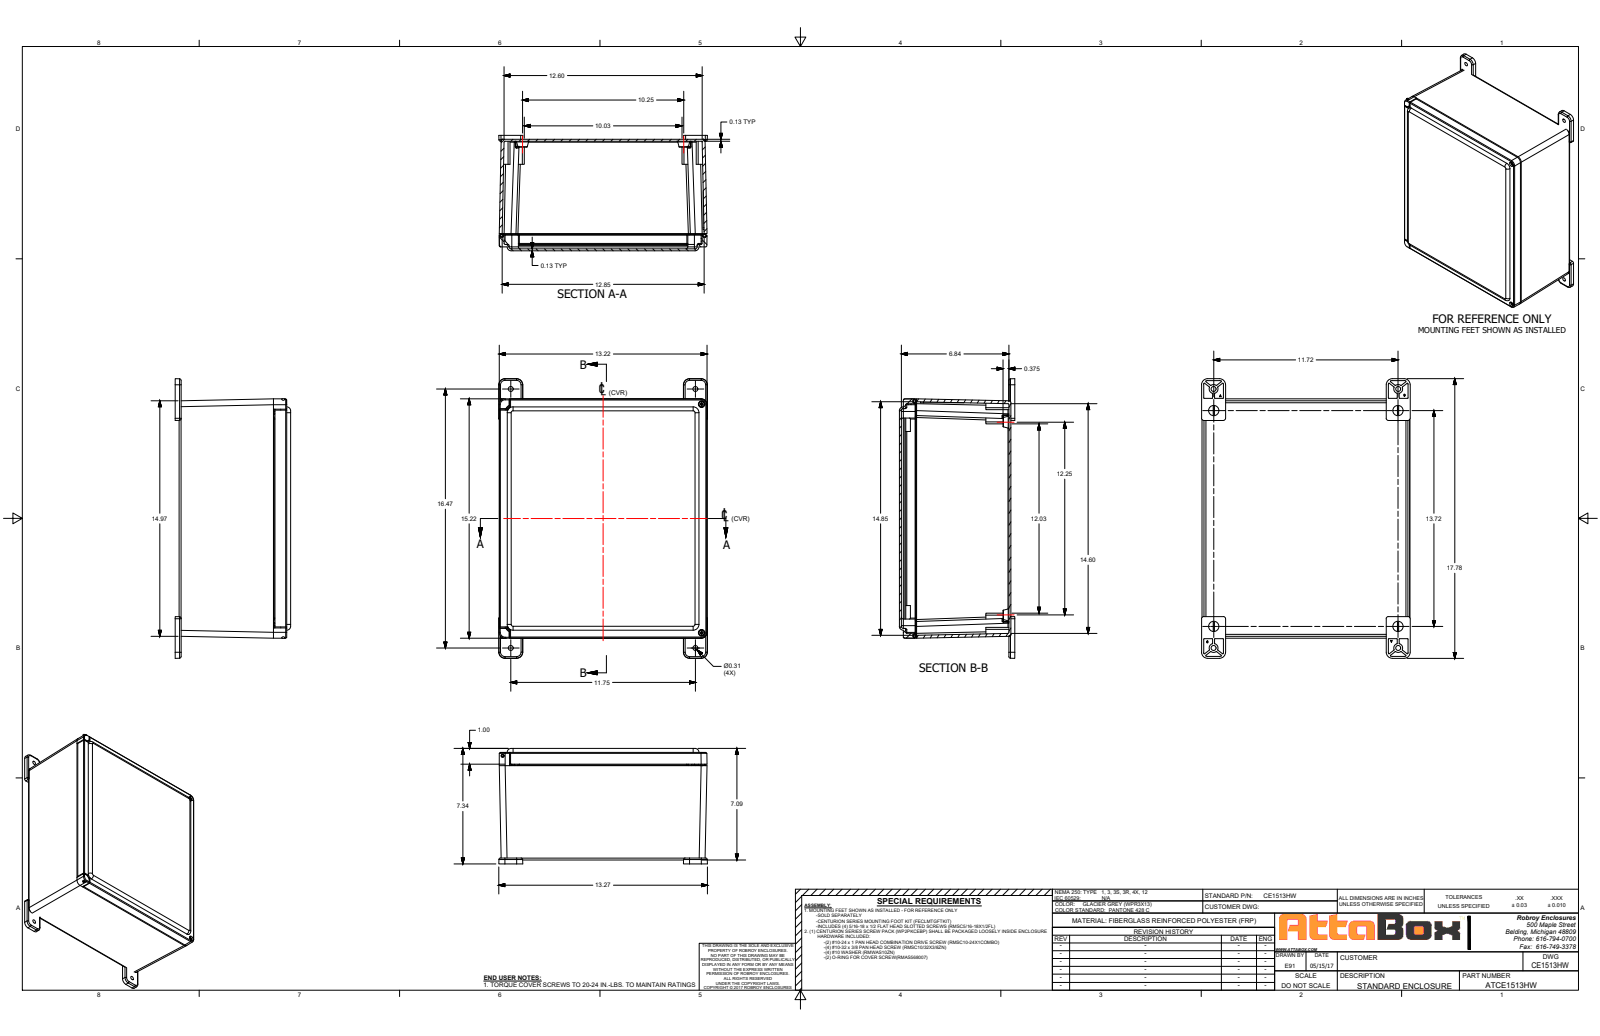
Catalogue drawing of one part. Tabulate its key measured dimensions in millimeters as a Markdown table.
| quantity | value |
| --- | --- |
| part name | CE1513HW |
| STEP written by | SolidWorks 2018 (AUTOMOTIVE_DESIGN) |
| units | millimeters |
| bodies | 30 solids, 1494 faces (658 planar, 424 cylindrical, 412 other) |
| overall size | 451.7 × 337.1 × 186.5 |
| volume | 2 348 000 mm³ |
| surface area | 1 115 000 mm² |
| round holes (diameter × count) | 4 × 6, 7.1 × 6, 8 × 4, 8 × 4, 8.7 × 4, 13.5 × 4, 2.4 × 2, 2.9 × 2, 4 × 2, 4.7 × 2, 4.8 × 2, 5.6 × 2 |
| round bosses / shafts (diameter × count) | 6.9 × 6, 5.8 × 4, 9.5 × 2, 9.5 × 2, 4.6 × 2, 3.5 × 2, 3.2 × 2, 3.2 × 2 |
| partial cylindrical surfaces (radius × count) | 0.8 × 60, 0.8 × 56, 3.2 × 44, 1.6 × 23, 6.4 × 16, 2.5 × 12, 9.5 × 10, 1.5 × 8 |
| main face-to-face distances | 3.2, 177, 4.7, 180.2, 173.8, 3.2, 6.4, 173.8, 170.7, 19.1 |
| hole center spacings | 26.4, 26.6, 34.9, 56.8, 279.7, 284.5, 300.1, 330.4 |
